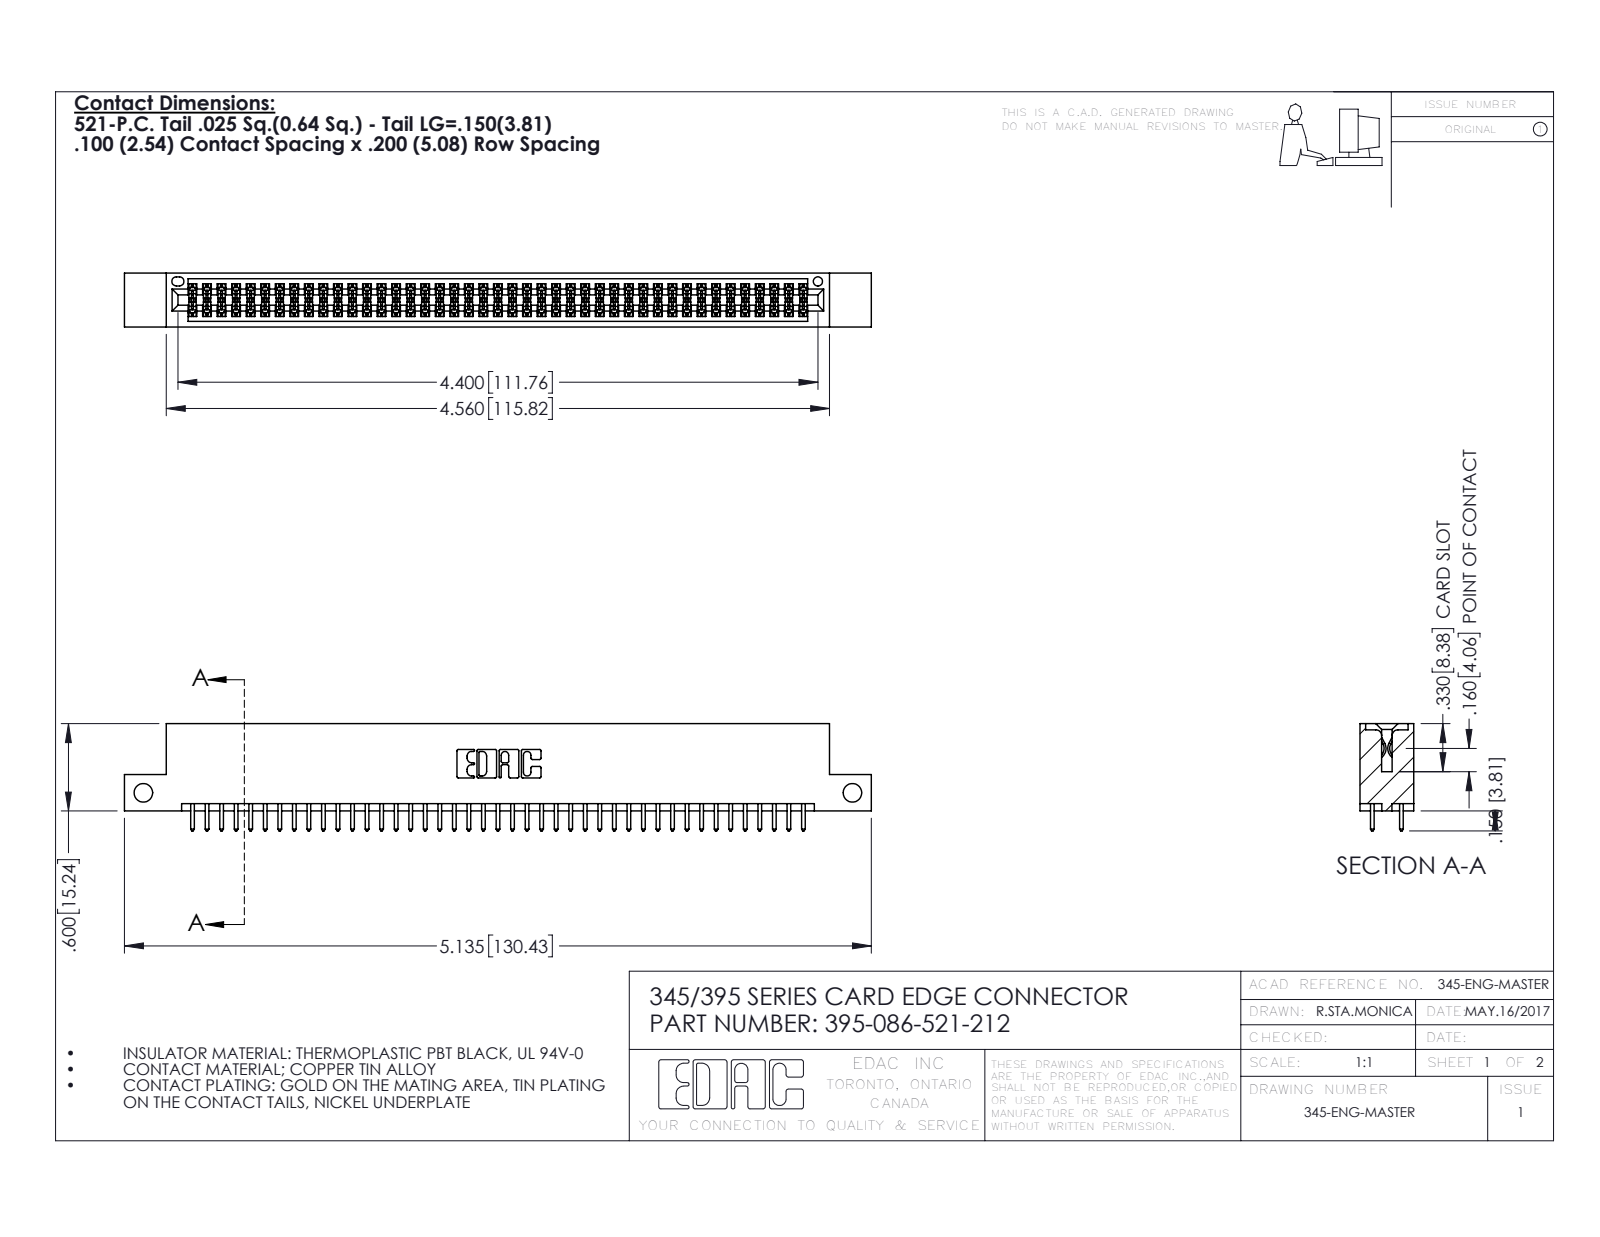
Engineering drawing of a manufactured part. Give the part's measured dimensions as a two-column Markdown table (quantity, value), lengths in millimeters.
| quantity | value |
| --- | --- |
| part name | 345 Part_Flush Mounting Lugs - Side Mount; 395-086-521-212; 345-292-001_345-293-121 |
| STEP written by | SolidWorks 2016 (CONFIG_CONTROL_DESIGN) |
| units | millimeters |
| bodies | 87 solids, 4426 faces (2918 planar, 1508 cylindrical, 0 other) |
| overall size | 130.4 × 18.7 × 9.4 |
| volume | 12 600 mm³ |
| surface area | 18 220 mm² |
| round holes (diameter × count) | 3.3 × 2, 1.6 × 1 |
| partial cylindrical surfaces (radius × count) | 0.2 × 129, 0.3 × 86, 0.3 × 22, 0.2 × 6, 0.8 × 6, 0.7 × 3, 0.4 × 2, 0.5 × 2 |
| main face-to-face distances | 7.6, 1.8, 5.1, 9.4, 2.5, 6.9, 0.6, 5.7, 4.4, 3.8 |
| hole center spacings | 123.8 |
